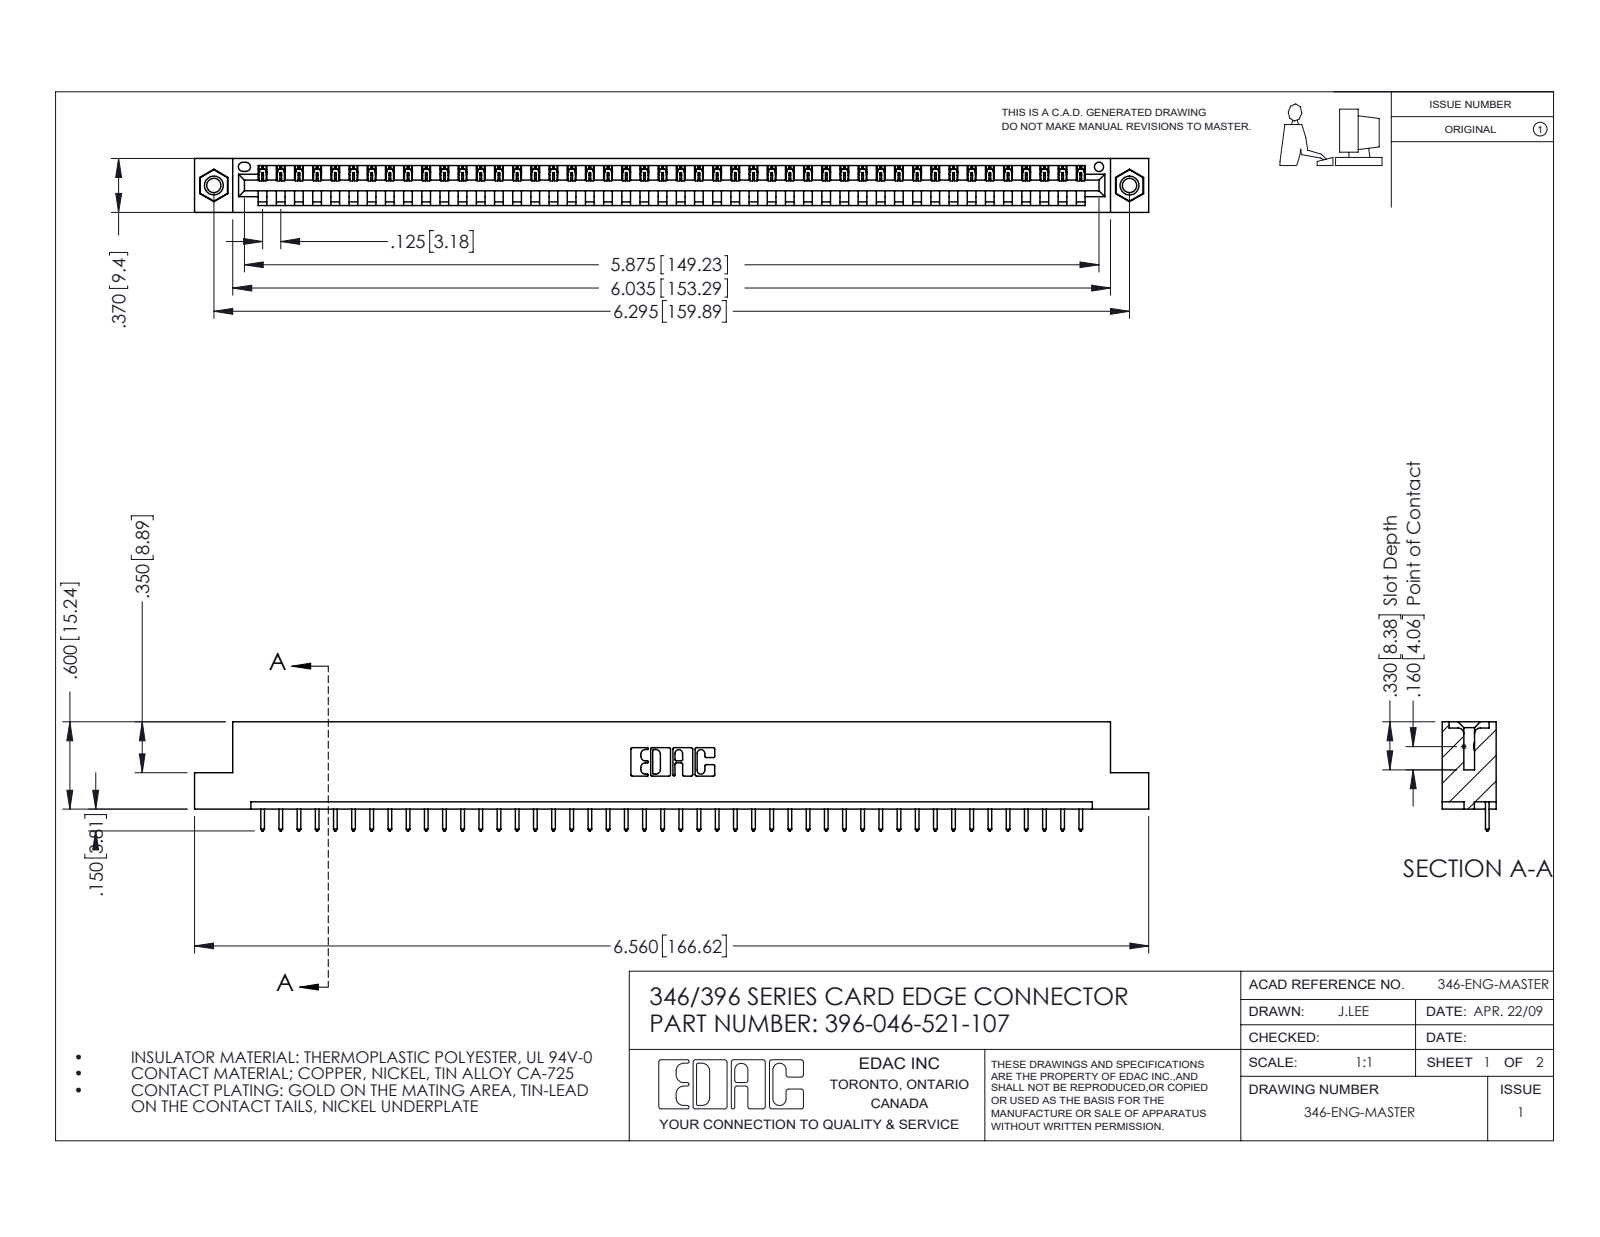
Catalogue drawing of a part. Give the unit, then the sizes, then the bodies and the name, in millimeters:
Units: millimetres
Overall size (bounding box): 166.6 × 19.1 × 9.4
Round holes (diameter × count): ⌀2.5 ×2, ⌀3.2 ×2, ⌀4 ×2, ⌀1.6 ×1
Round bosses / shafts (diameter × count): ⌀3.9 ×2
Partial cylindrical surfaces — rounded edges, fillets, slot ends (radius × count): R0.2 ×92, R0.3 ×92, R0.3 ×22, R0.2 ×6, R0.8 ×6, R0.7 ×3, R0.8 ×2, R1 ×2
Main face-to-face distances: 1.2, 8.2, 9.4, 6.4, 1.8, 7.6, 0.6, 3.8, 5.6, 2.5
Hole centre spacings: 6.2, 154.6, 159.9
Volume: 15 800 mm³ · Surface area: 19 350 mm²
Bodies: 49 solids, 2850 faces (1948 planar, 886 cylindrical, 16 other)
Part name (STEP PRODUCT): 345-292-001_345-293-121; 396-046-521-107; 346 Part_Flush Mounting Lugs - 0.156 Dia-TI; 345-250-001_345-250-005-103
STEP written by: SolidWorks 2016 (CONFIG_CONTROL_DESIGN)
